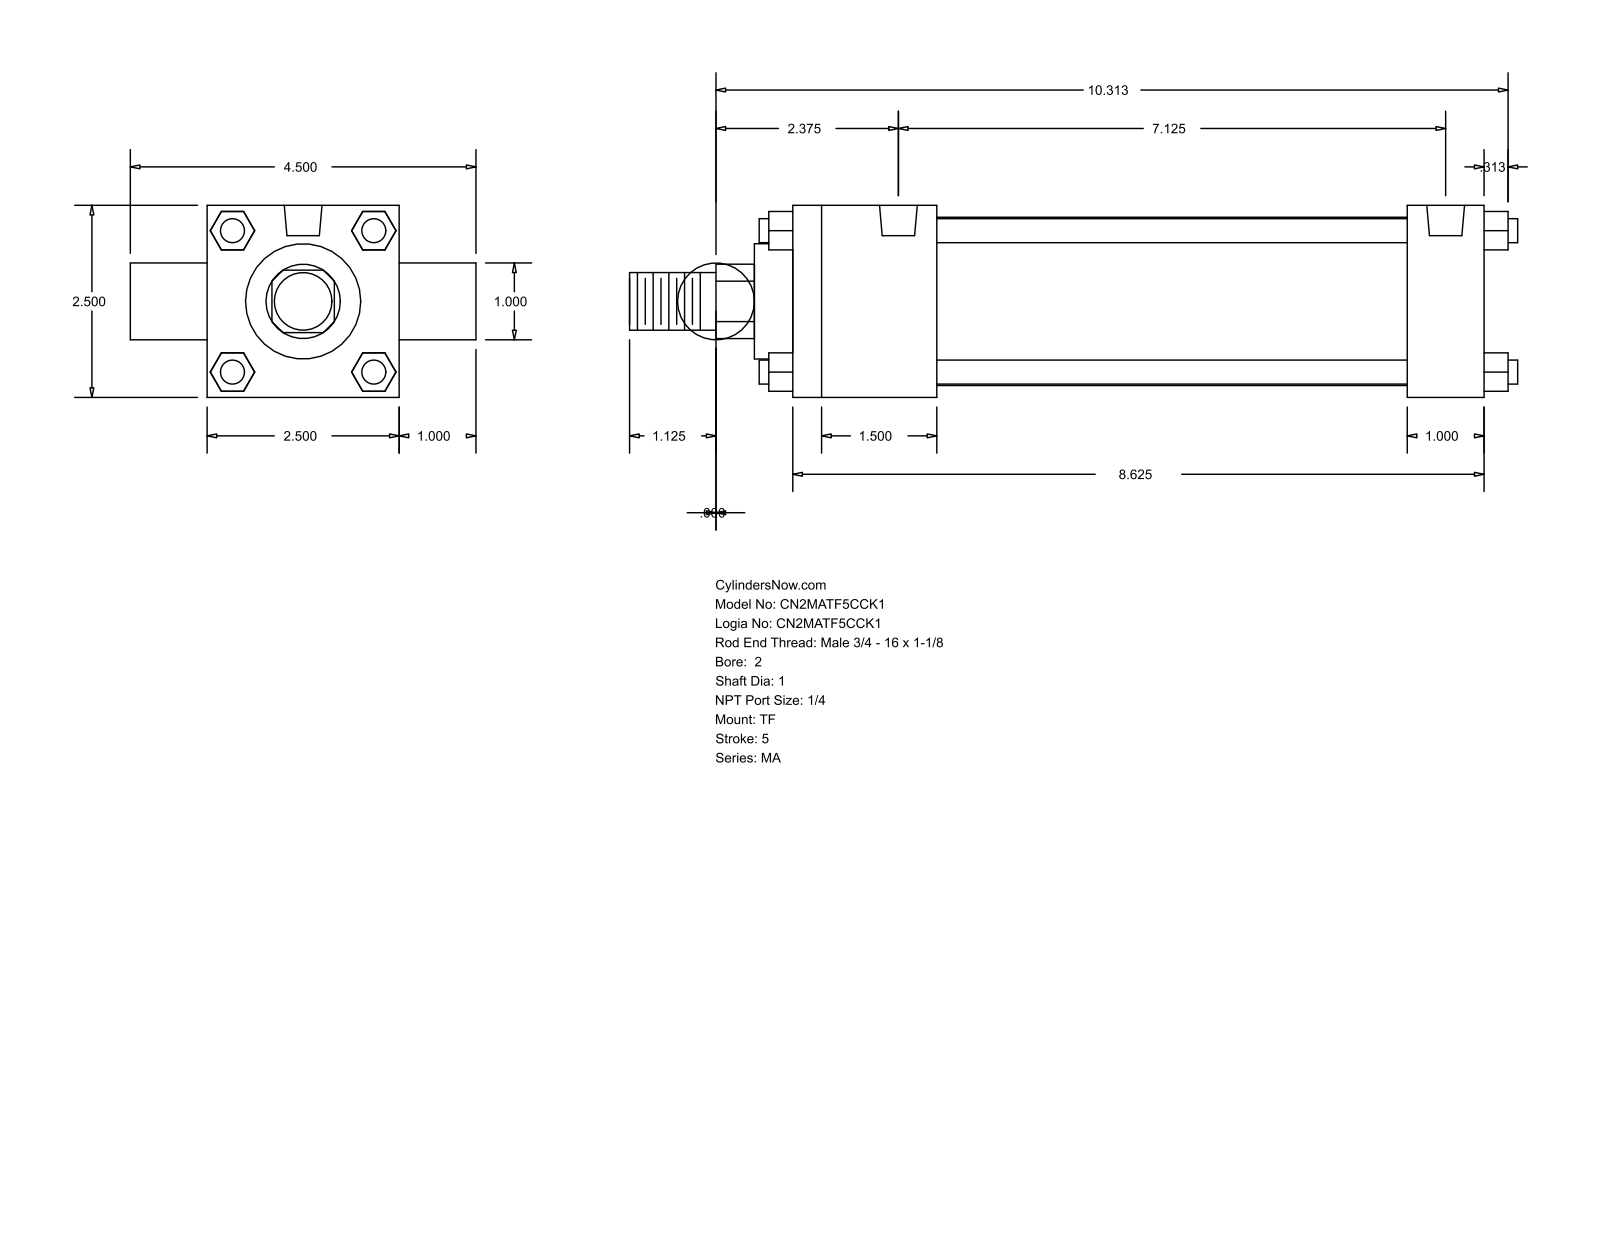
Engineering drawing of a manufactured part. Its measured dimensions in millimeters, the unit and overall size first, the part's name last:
Units: millimetres
Overall size (bounding box): 293.69 × 114.3 × 63.5
Round holes (diameter × count): ⌀7.94 ×3, ⌀12.49 ×2
Round bosses / shafts (diameter × count): ⌀7.94 ×4, ⌀25.4 ×2, ⌀55.63 ×1, ⌀38.1 ×1, ⌀19.05 ×1
Partial cylindrical surfaces — rounded edges, fillets, slot ends (radius × count): R12.29 ×1
Main face-to-face distances: 63.5, 25.4, 228.6, 12.7, 47.63, 203.2, 155.57, 180.97, 88.9, 40.47
Hole centre spacings: 180.97
Bodies: 0 solids, 120 faces (92 planar, 28 cylindrical, 0 other)
Part name (STEP PRODUCT): MA_TF__0200_1
STEP written by: GSSL Pune (CONFIG_CONTROL_DESIGN)
